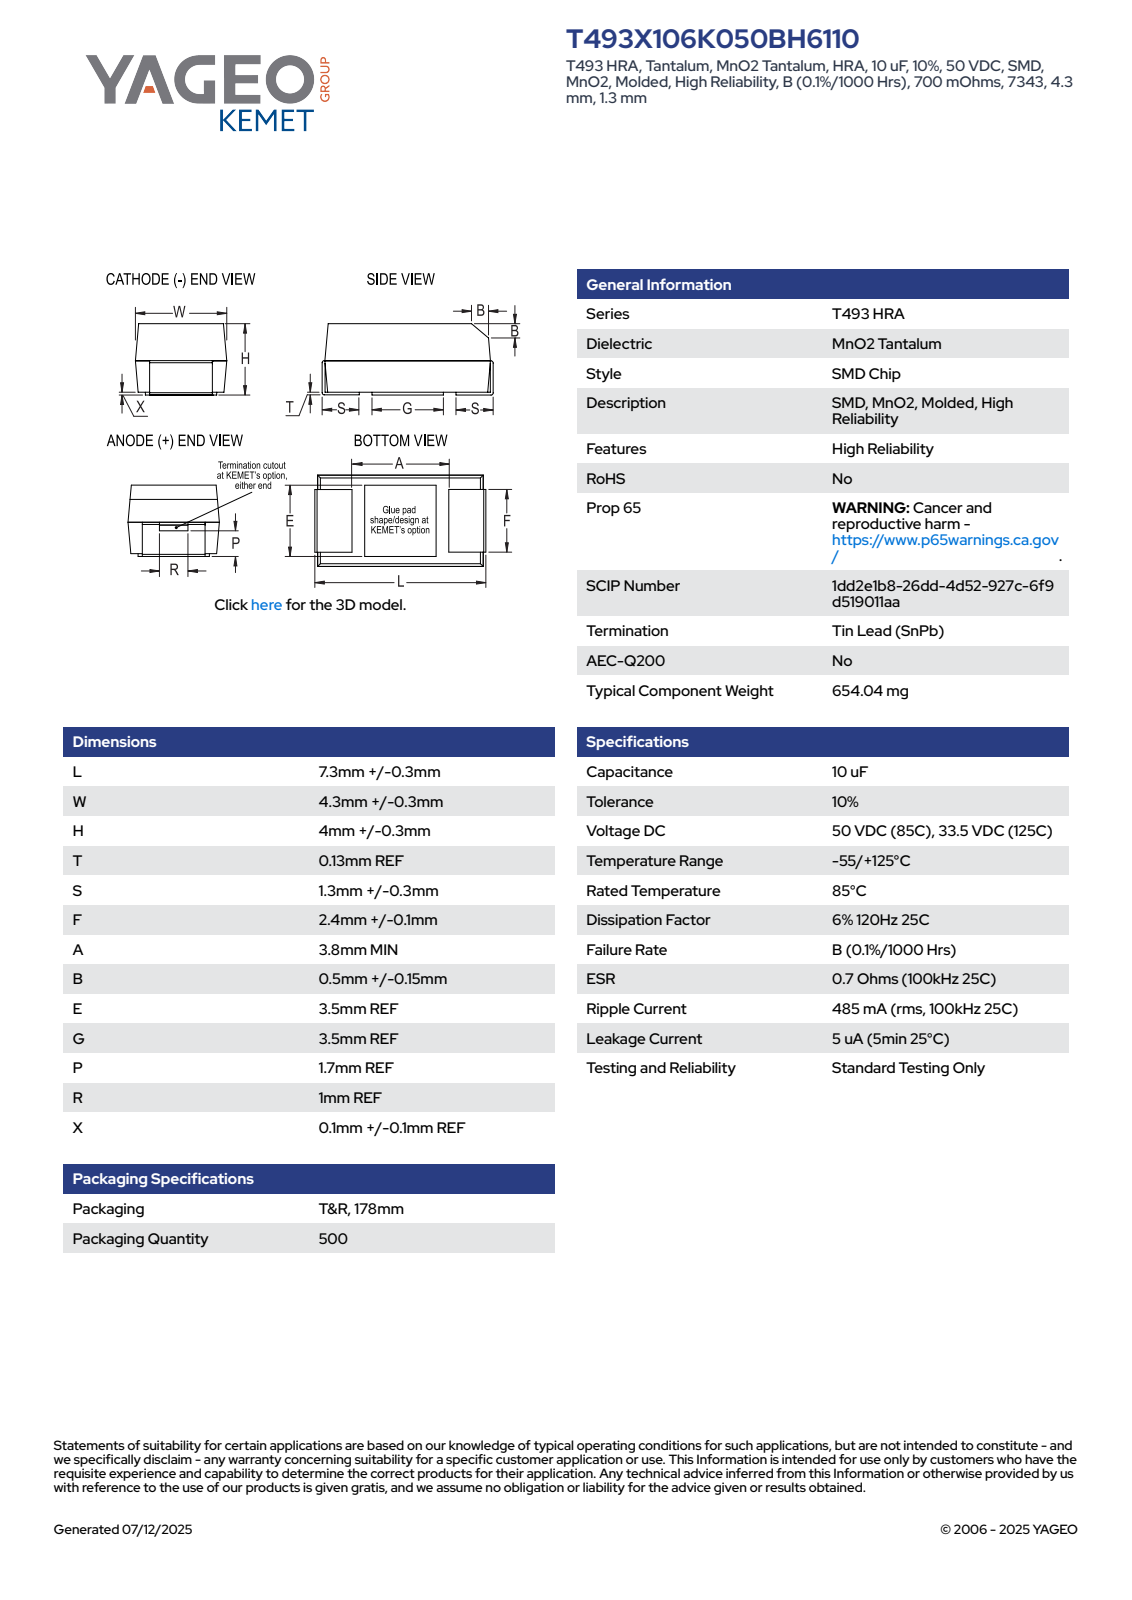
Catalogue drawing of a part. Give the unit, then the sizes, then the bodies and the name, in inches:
Units: inches
Overall size (bounding box): 0.299 × 0.181 × 0.169
Main face-to-face distances: 0.18, 0.085, 0.079, 0.164, 0.288, 0.294, 0.083, 0.168, 0.084, 0.169
Volume: 0.008 in³ · Surface area: 0.4 in²
Bodies: 7 solids, 100 faces (95 planar, 5 cylindrical, 0 other)
Part name (STEP PRODUCT): CTSM_Case_Bottom_20; CTSM_Case_Cathode_20; CTSM_Case_Anode_20; CTSM_7343_L7.60W4.6H4.30S1.3F2.4R1P1.7B0.5 (+1 more)
STEP written by: SolidWorks 2014 (AUTOMOTIVE_DESIGN)
